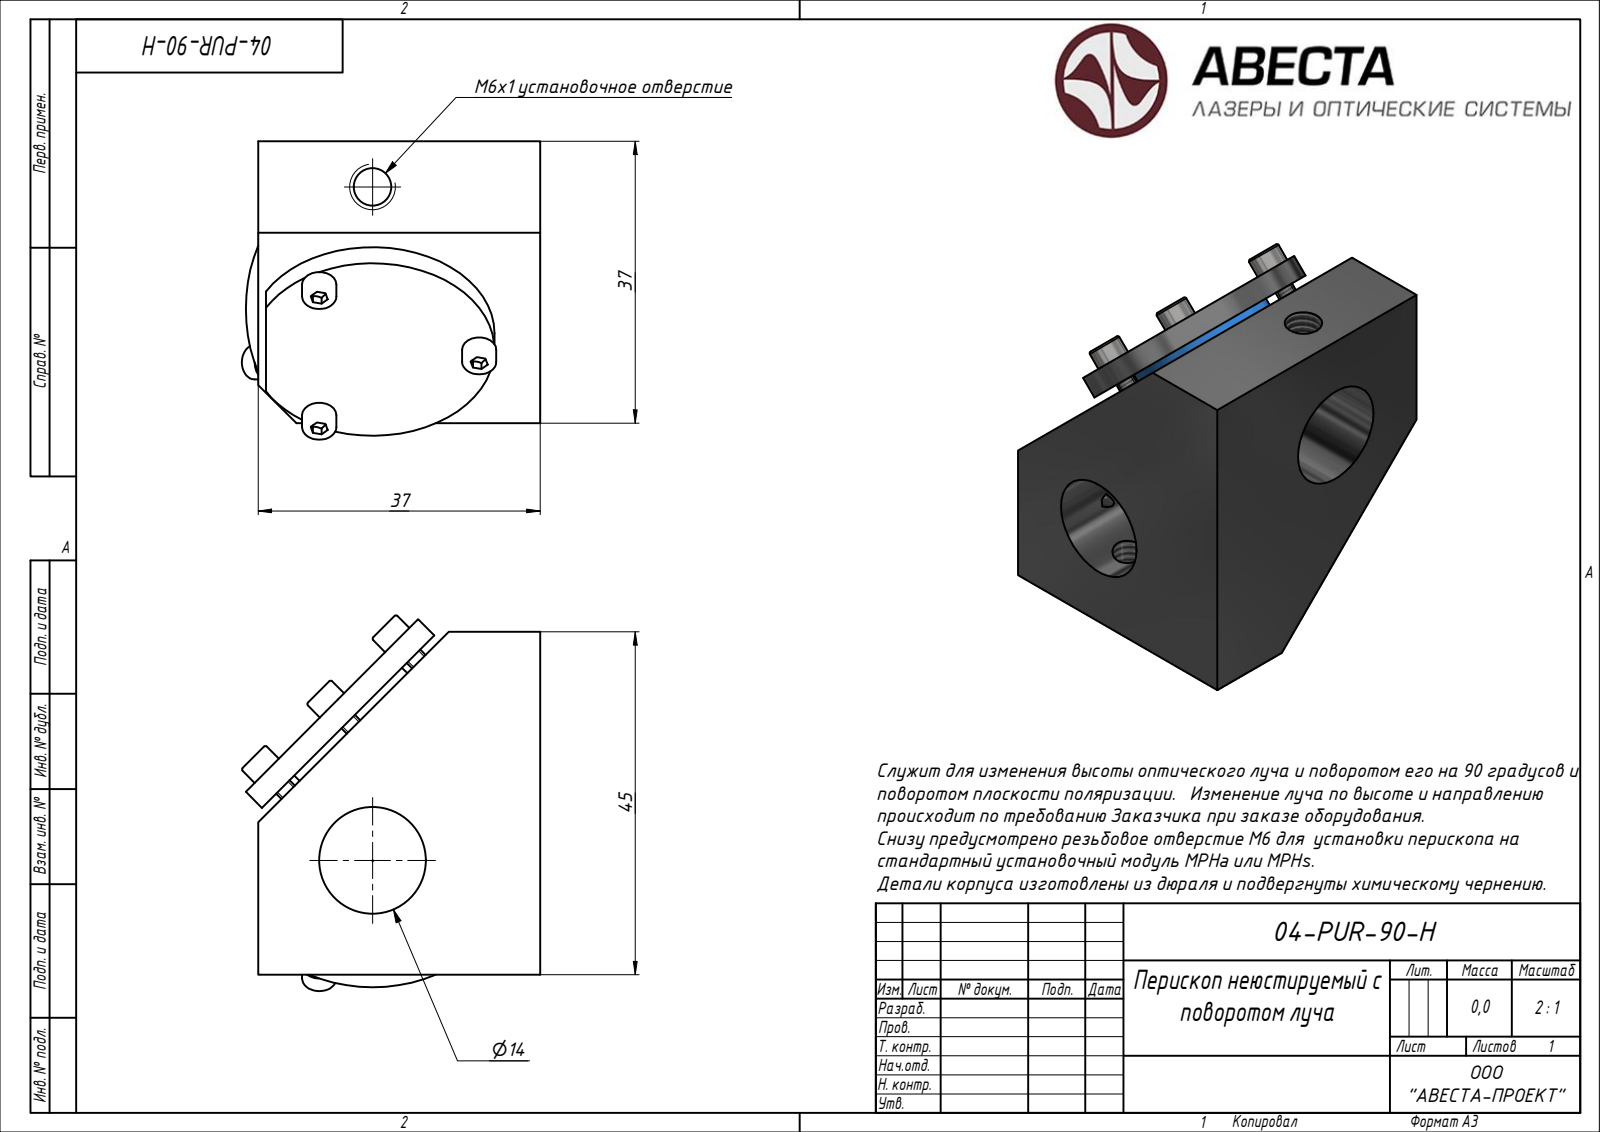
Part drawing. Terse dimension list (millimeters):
name: Block 01
written by: ST-DEVELOPER v15 (AUTOMOTIVE_DESIGN)
unit: mm
bodies: 12 solids, 250 faces (0 planar, 0 cylindrical, 250 other)
size: 49.31 × 39.16 × 39.16
